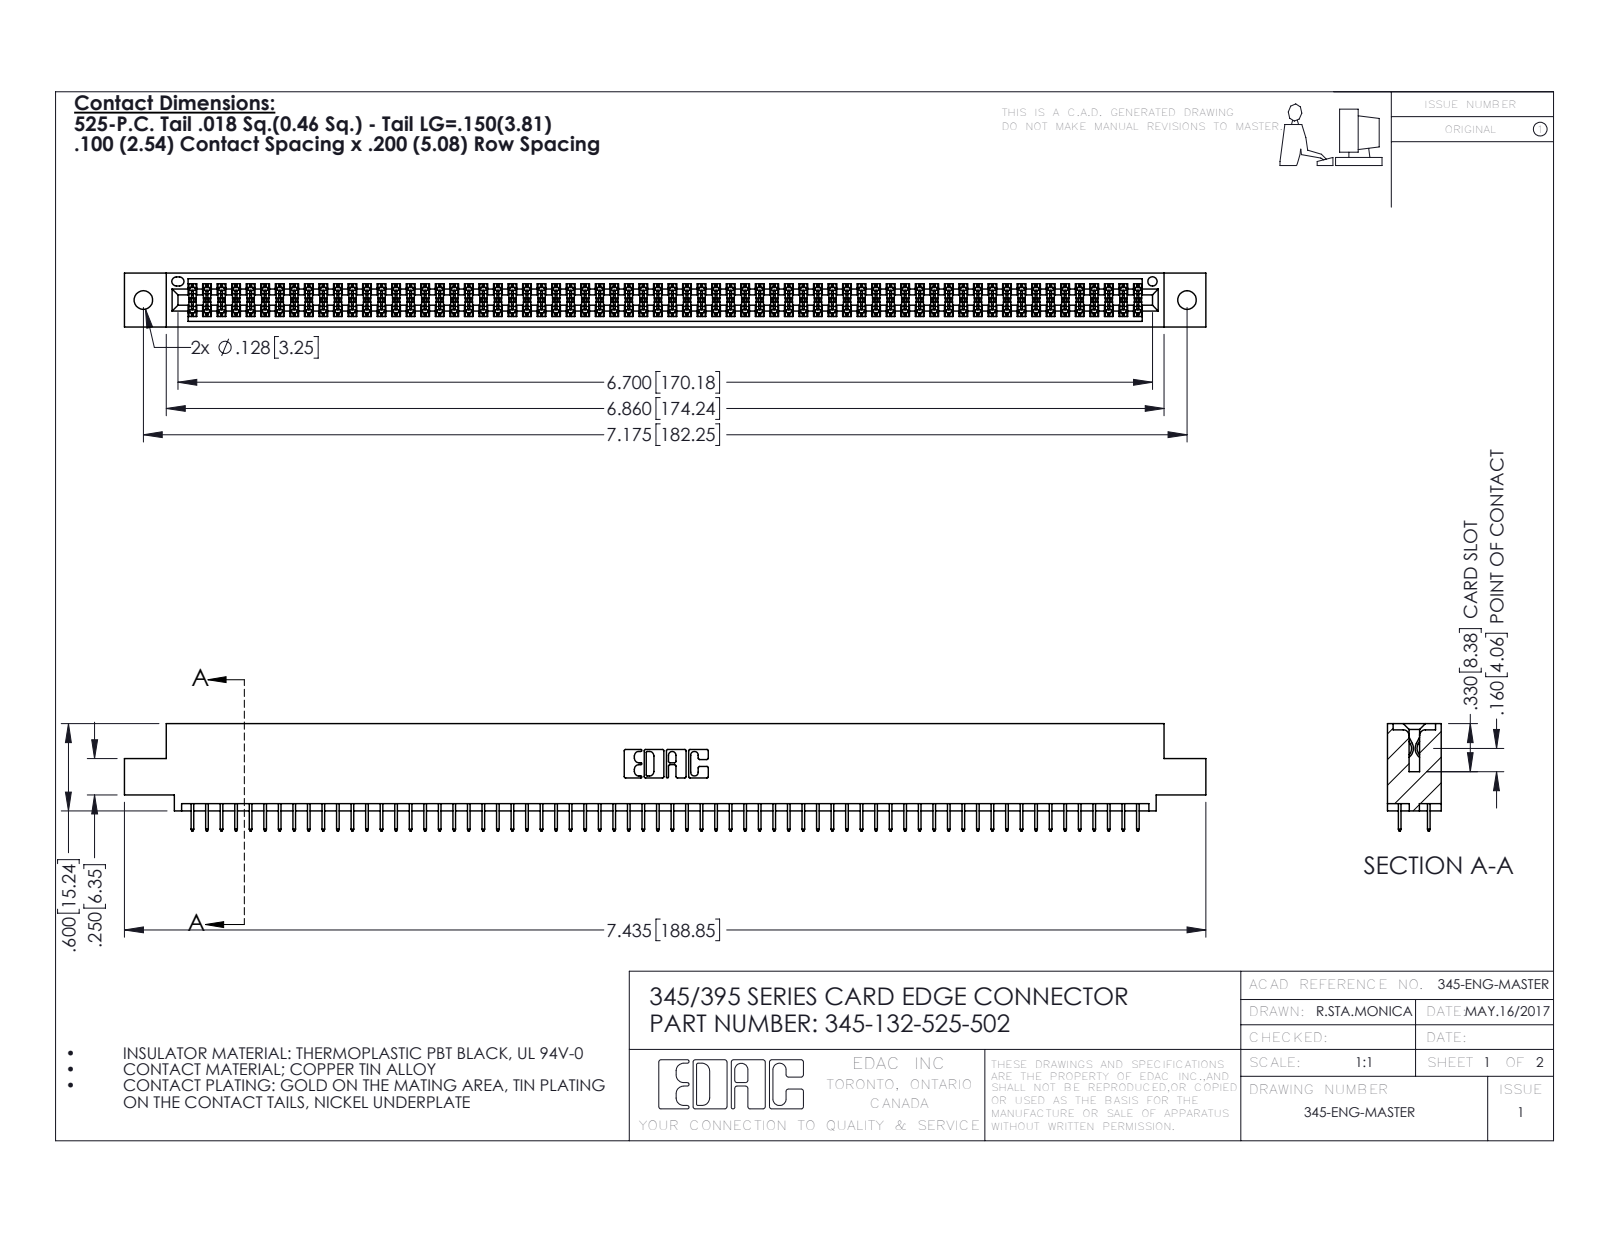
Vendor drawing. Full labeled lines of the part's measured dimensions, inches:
Part name (STEP PRODUCT): 345 Part_0.110 Offset - 0.128 Dia; 345-132-525-502; 345-292-001_345-293-125
STEP written by: SolidWorks 2020 (CONFIG_CONTROL_DESIGN)
Units: inches
Bodies: 133 solids, 7258 faces (5232 planar, 2026 cylindrical, 0 other)
Overall size (bounding box): 7.435 × 0.737 × 0.37
Volume: 1.113 in³ · Surface area: 41.22 in²
Round holes (diameter × count): ⌀0.128 ×2, ⌀0.064 ×1
Partial cylindrical surfaces — rounded edges, fillets, slot ends (radius × count): R0.006 ×263, R0.01 ×22, R0.007 ×6, R0.031 ×6, R0.026 ×3, R0.014 ×2, R0.019 ×2, R0.022 ×2
Main face-to-face distances: 0.072, 0.298, 0.2, 0.37, 0.098, 0.272, 0.025, 0.225, 0.072, 0.175
Hole centre spacings: 0.27, 6.939, 7.175
